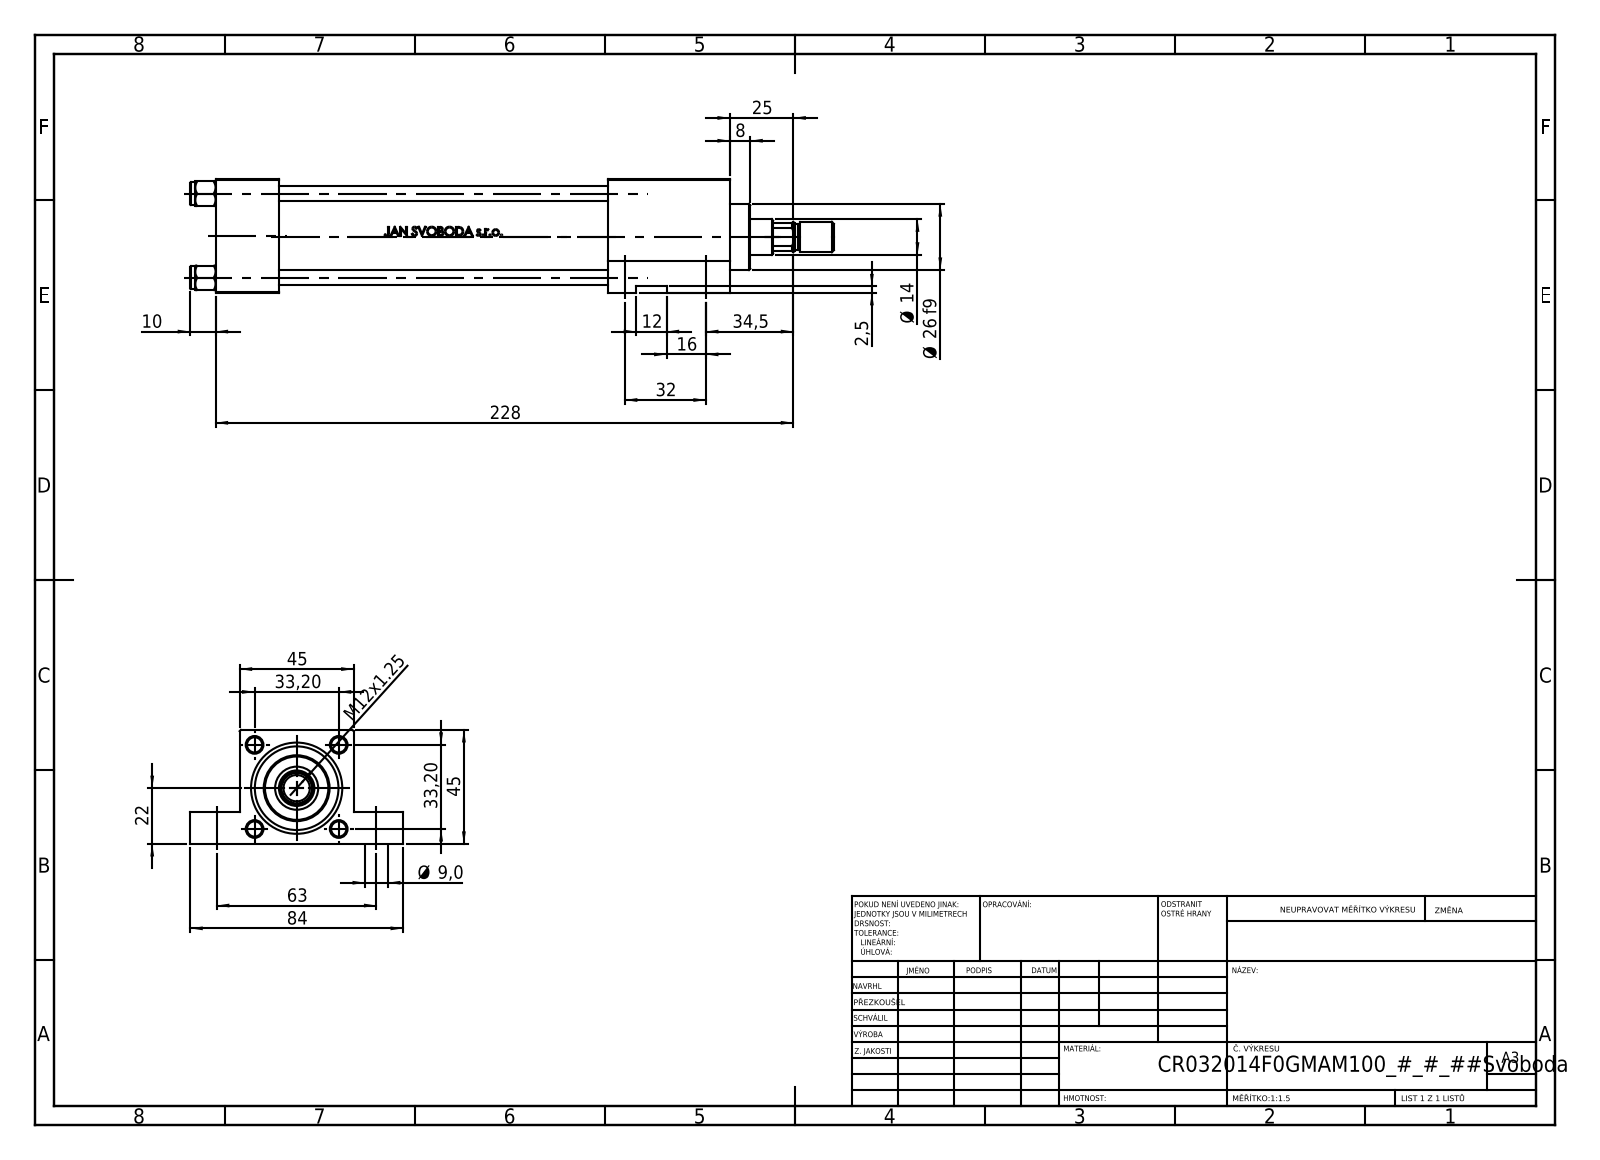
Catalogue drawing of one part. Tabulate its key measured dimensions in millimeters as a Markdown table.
| quantity | value |
| --- | --- |
| part name | ROD_END_AH; NUT_M5_F; V215CR_F_TYCINKA; V215CR_VCP_F (+2 more) |
| STEP written by | SolidWorks 2019 (CONFIG_CONTROL_DESIGN) |
| units | millimeters |
| bodies | 12 solids, 1116 faces (440 planar, 130 cylindrical, 546 other) |
| overall size | 254 × 84 × 45 |
| volume | 261 395 mm³ |
| surface area | 100 707 mm² |
| round holes (diameter × count) | 6 × 4, 9 × 4, 7 × 2, 20 × 2, 6.5 × 1, 13 × 1, 13.16 × 1, 14 × 1, 17 × 1, 24 × 1, 32 × 1, 33 × 1 |
| round bosses / shafts (diameter × count) | 9 × 4, 38 × 1, 26 × 1, 12 × 1, 10 × 1 |
| partial cylindrical surfaces (radius × count) | 6.5 × 1 |
| main face-to-face distances | 45, 25, 178, 203, 32.5, 155, 130, 48, 12.5, 10 |
| hole center spacings | 33.2, 23.13, 23.83, 32, 46.95, 63, 70.66, 155.5 |
